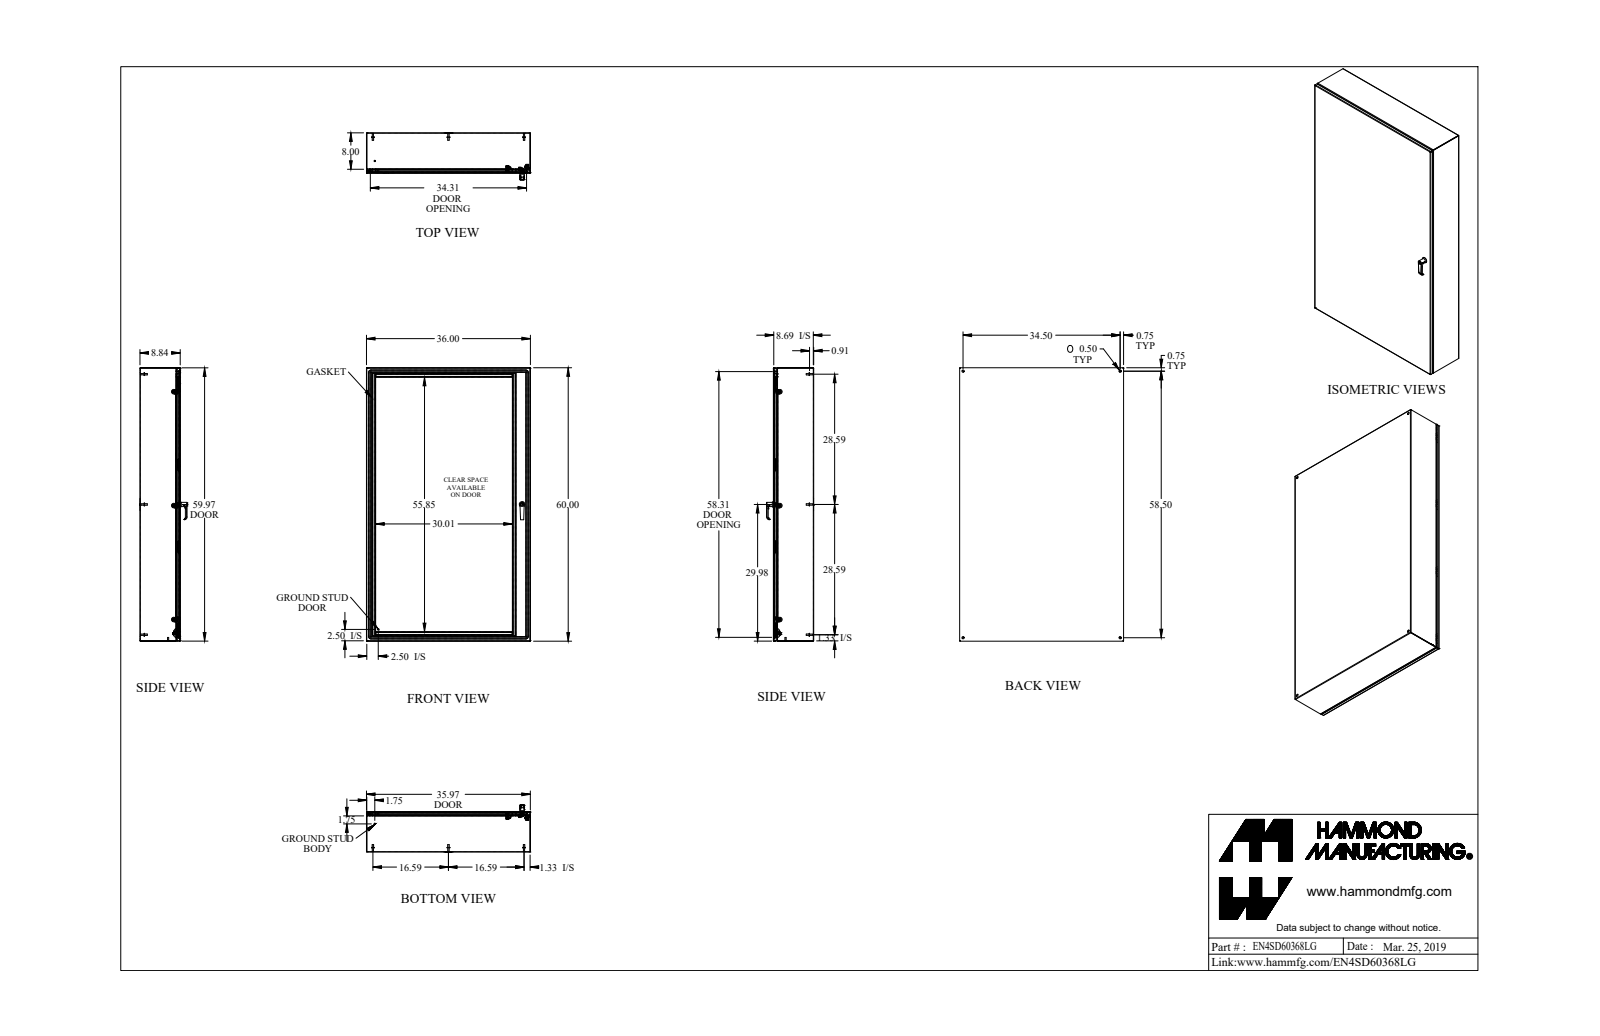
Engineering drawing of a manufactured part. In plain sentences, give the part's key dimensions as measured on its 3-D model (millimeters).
The part is named "EN4SD60368LG_Default". Its 3-D file was written by "SolidWorks 2019 (CONFIG_CONTROL_DESIGN)". It is 61 solids with 1731 faces: 755 planar, 644 cylindrical and 332 other. Overall it measures 1524 by 914.4 by 263.3 millimeters. Its volume is 8 151 000 cubic millimeters and its surface area 9 056 000 square millimeters. Round holes: 6 of diameter 4.5, 4 of diameter 5, 4 of diameter 12.7, 3 of diameter 6.4, 3 of diameter 6.7, 3 of diameter 10.5, 2 of diameter 6.5, 2 of diameter 8, 2 of diameter 10, 1 of diameter 4.4, 1 of diameter 6.1, 1 of diameter 6.1. Round bosses or shafts: 9 of diameter 15.9, 8 of diameter 8, 8 of diameter 6.9, 7 of diameter 6.4, 6 of diameter 9.5, 6 of diameter 4, 3 of diameter 25.4, 2 of diameter 16. Partial cylindrical surfaces (rounded edges, fillets, slot ends): 24 of radius 1.1, 21 of radius 1.6, 20 of radius 0.9, 20 of radius 2.7, 15 of radius 0.8, 10 of radius 2.4, 9 of radius 0.4, 8 of radius 0.2. The main face-to-face distances are 1.8, 222.6, 220.8, 224.5, 912.6, 1522.2, 910.7, 914.4, 1520.3, 1524. The hole center spacings are 635, 111.7, 855.9, 876.3, 1270, 1377.8, 1485.9, 1618.2.
